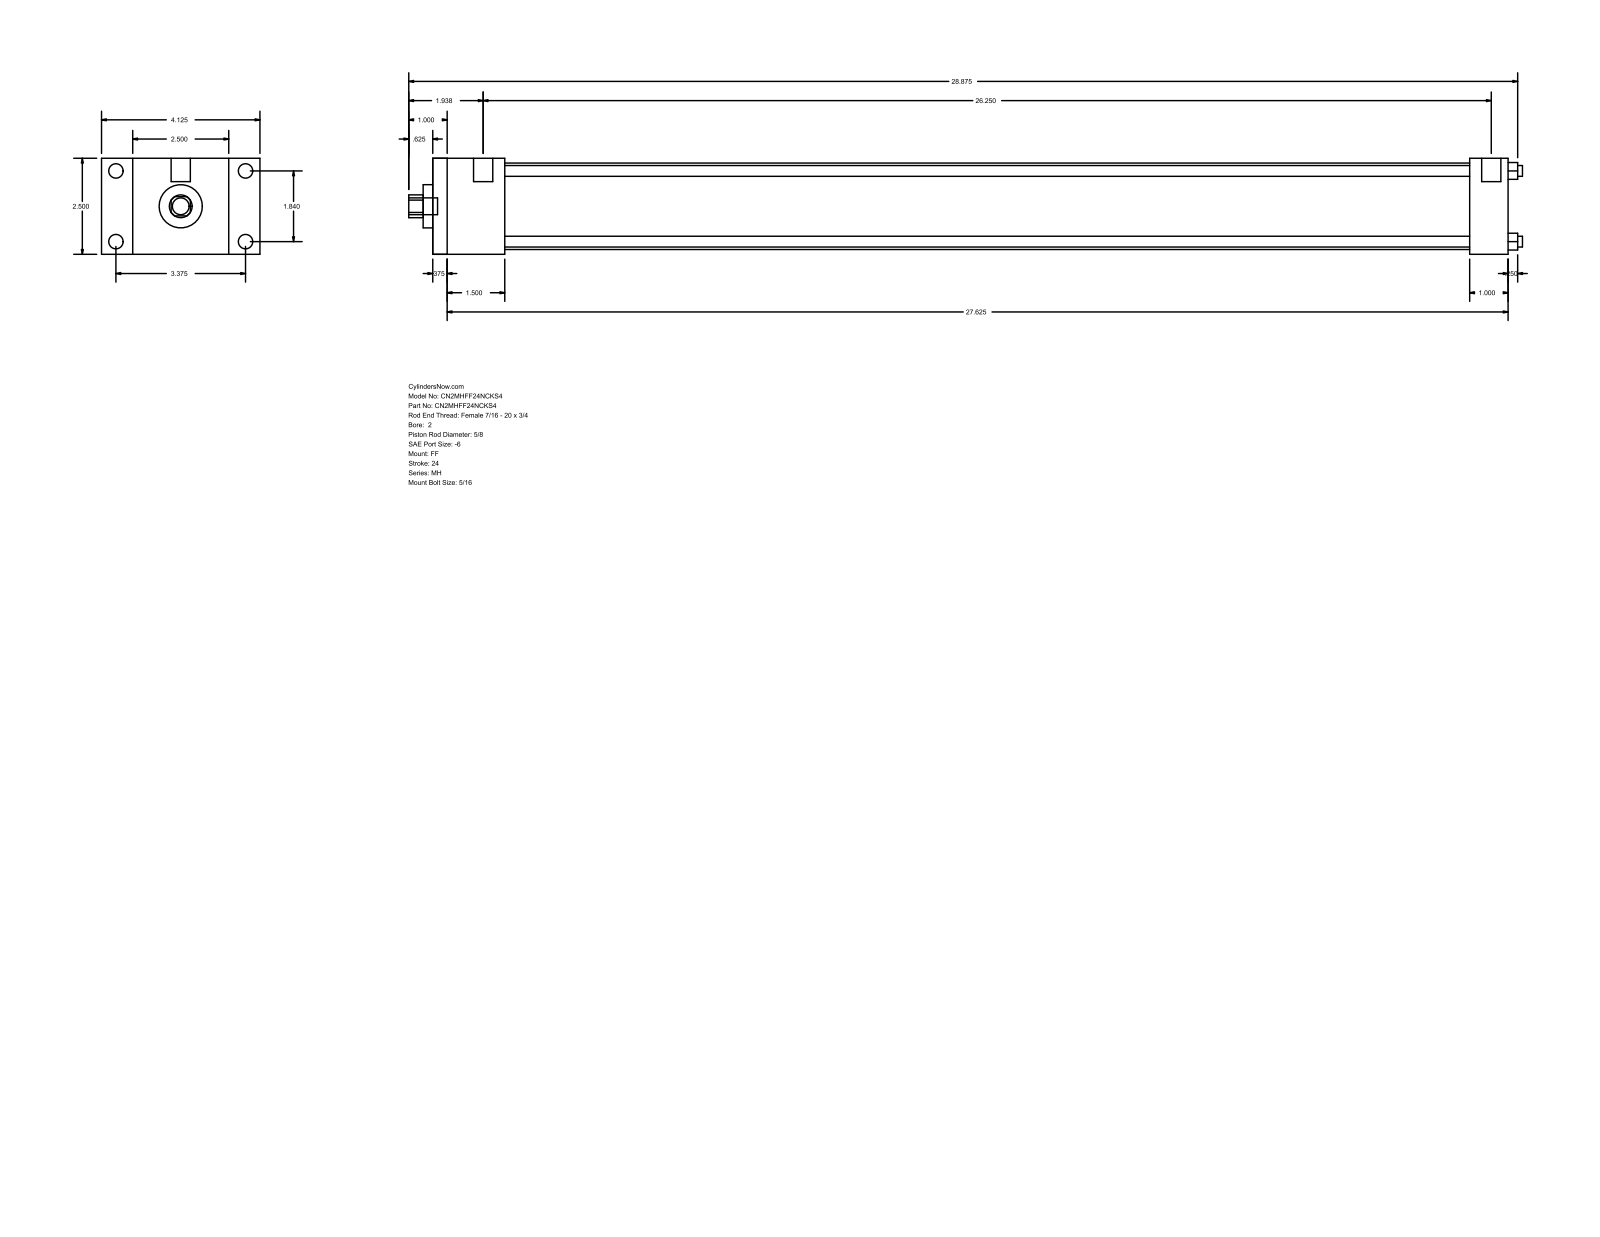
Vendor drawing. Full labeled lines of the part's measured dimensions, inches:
Part name (STEP PRODUCT): MH_FF__0200_0.625
STEP written by: GSSL Pune (CONFIG_CONTROL_DESIGN)
Units: inches
Bodies: 0 solids, 92 faces (64 planar, 28 cylindrical, 0 other)
Overall size (bounding box): 29 × 4.125 × 2.5
Round holes (diameter × count): ⌀0.281 ×4, ⌀0.625 ×1, ⌀1.125 ×1, ⌀2.25 ×1
Round bosses / shafts (diameter × count): ⌀0.375 ×4, ⌀0.219 ×4, ⌀0.5 ×2, ⌀0.437 ×1
Partial cylindrical surfaces — rounded edges, fillets, slot ends (radius × count): R0.297 ×1
Main face-to-face distances: 2.5, 28, 0.375, 27.625, 1.5, 1.875, 27, 26.625, 25.125, 26.125
Hole centre spacings: 1.301, 1.84, 2.602
